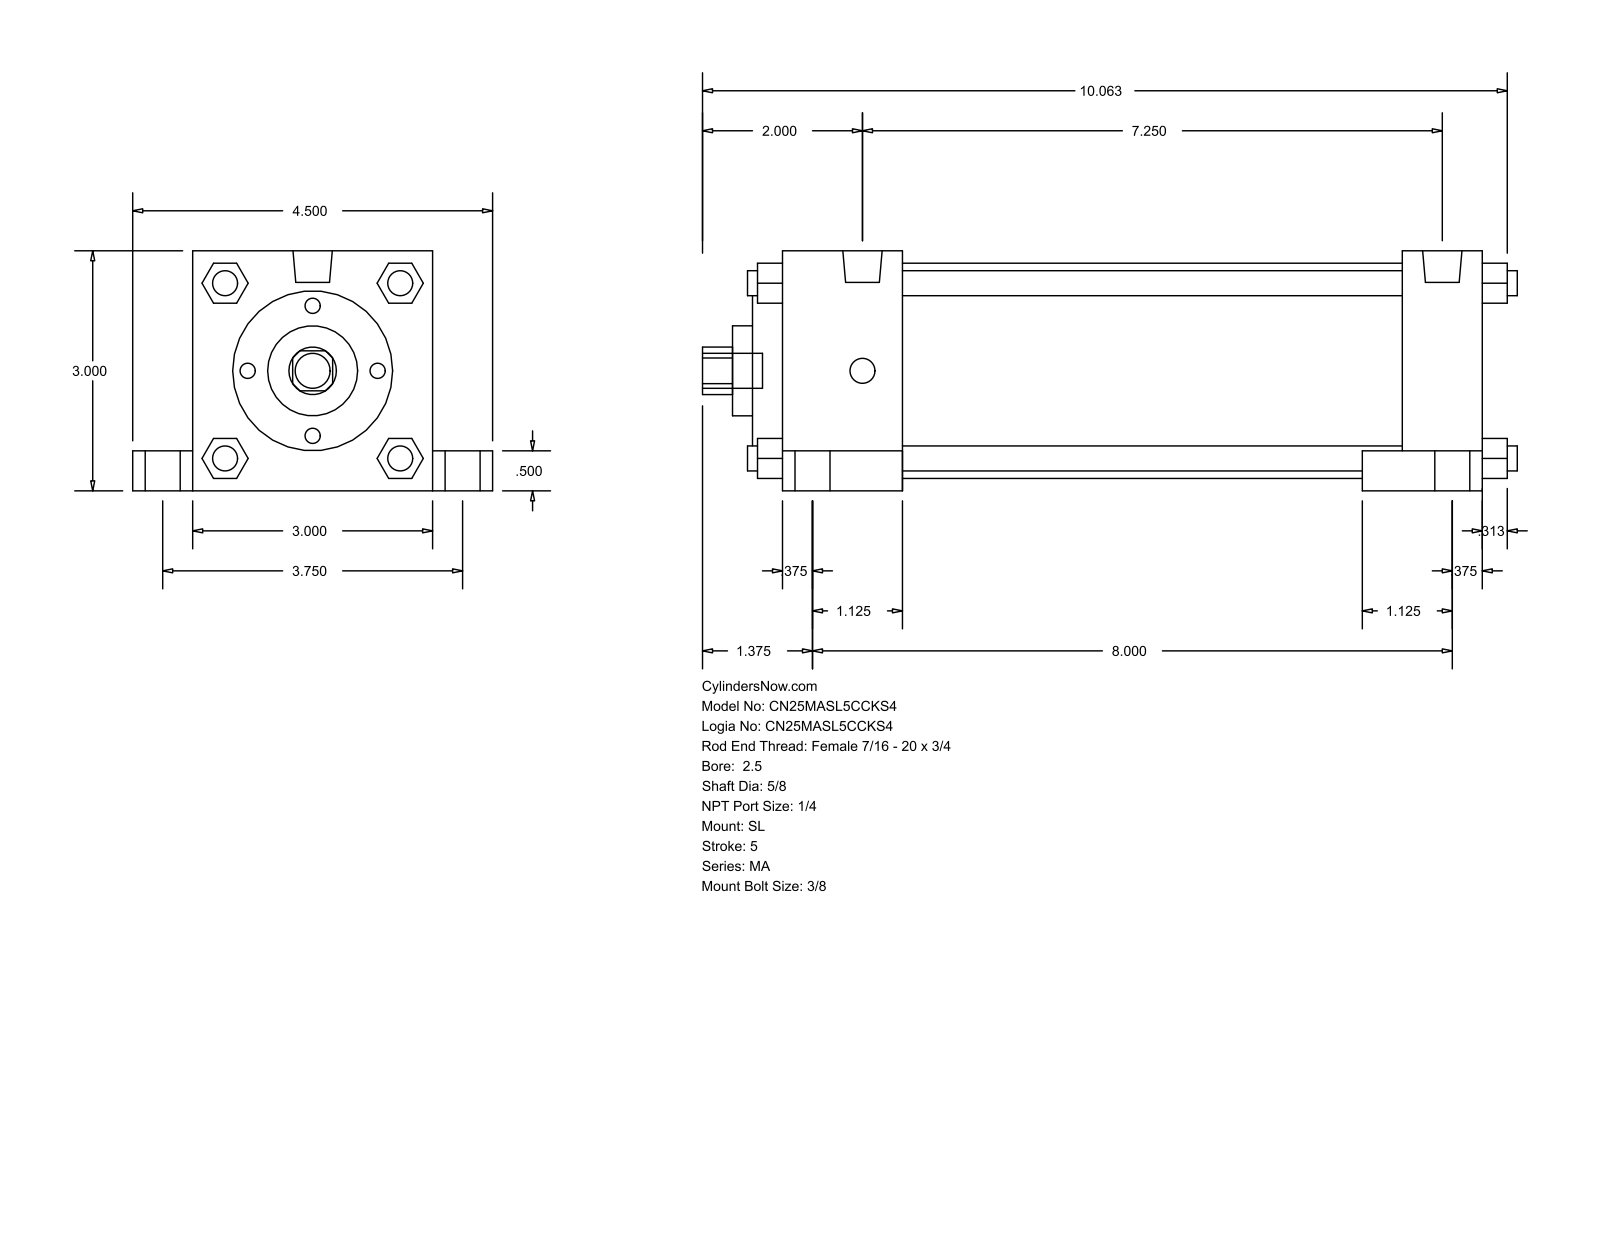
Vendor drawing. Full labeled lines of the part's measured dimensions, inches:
Part name (STEP PRODUCT): MA_SL__0250_0.625
STEP written by: GSSL Pune (CONFIG_CONTROL_DESIGN)
Units: inches
Bodies: 0 solids, 150 faces (113 planar, 37 cylindrical, 0 other)
Overall size (bounding box): 10.187 × 4.5 × 3
Round holes (diameter × count): ⌀0.625 ×1, ⌀1.125 ×1, ⌀2 ×1, ⌀2.69 ×1
Round bosses / shafts (diameter × count): ⌀0.313 ×8, ⌀0.437 ×5, ⌀0.687 ×4, ⌀0.492 ×2
Partial cylindrical surfaces — rounded edges, fillets, slot ends (radius × count): R0.297 ×1
Main face-to-face distances: 3, 8.75, 0.5, 6.25, 1, 1.5, 7.25, 7.75, 0.75, 2.5
